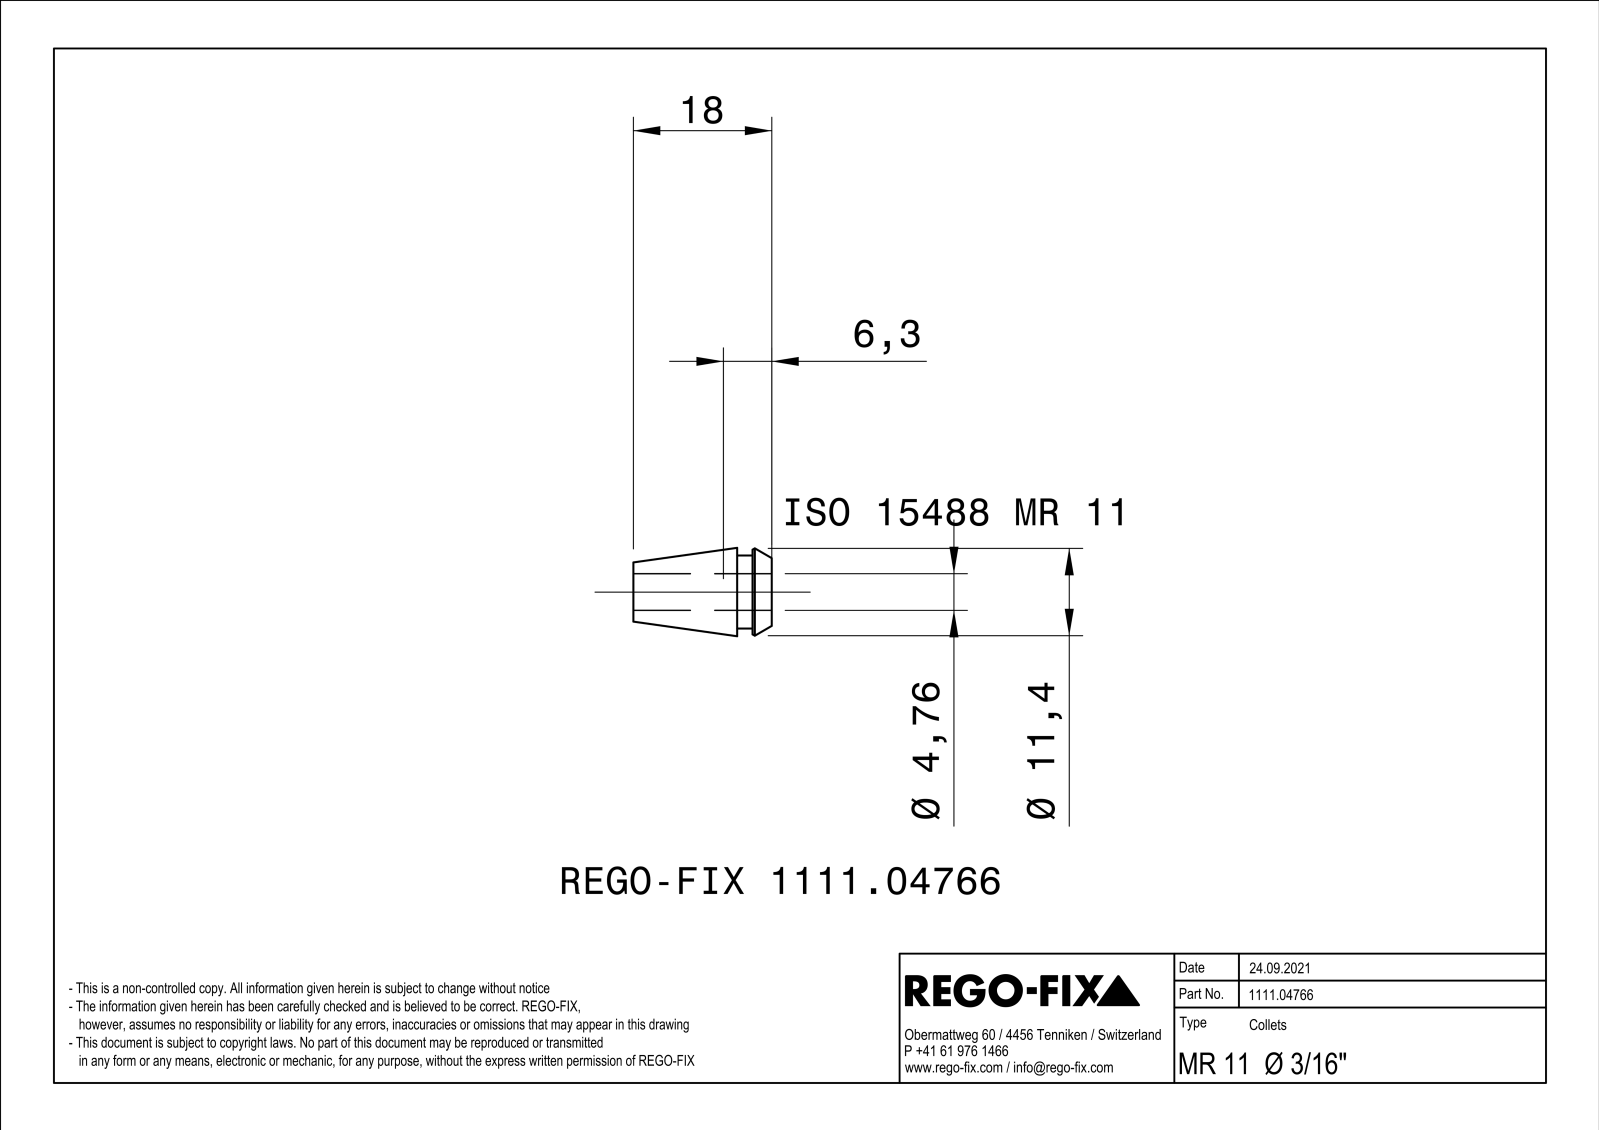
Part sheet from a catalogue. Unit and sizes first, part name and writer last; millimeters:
Units: millimetres
Overall size (bounding box): 18 × 11.43 × 11.43
Round holes (diameter × count): ⌀4.76 ×1
Round bosses / shafts (diameter × count): ⌀11.44 ×1, ⌀9.5 ×1
Partial cylindrical surfaces — rounded edges, fillets, slot ends (radius × count): R0.23 ×18
Main face-to-face distances: 0.45, 0.46, 0.44, 4.5, 2.5, 2, 18, 15.5, 13.5
Volume: 824 mm³ · Surface area: 1 685 mm²
Bodies: 1 solid, 189 faces (55 planar, 43 cylindrical, 91 other)
Part name (STEP PRODUCT): NOCUT
STEP written by: SIEMENS PLM Software Solid Edge ST10 (AUTOMOTIVE_DESIGN)
